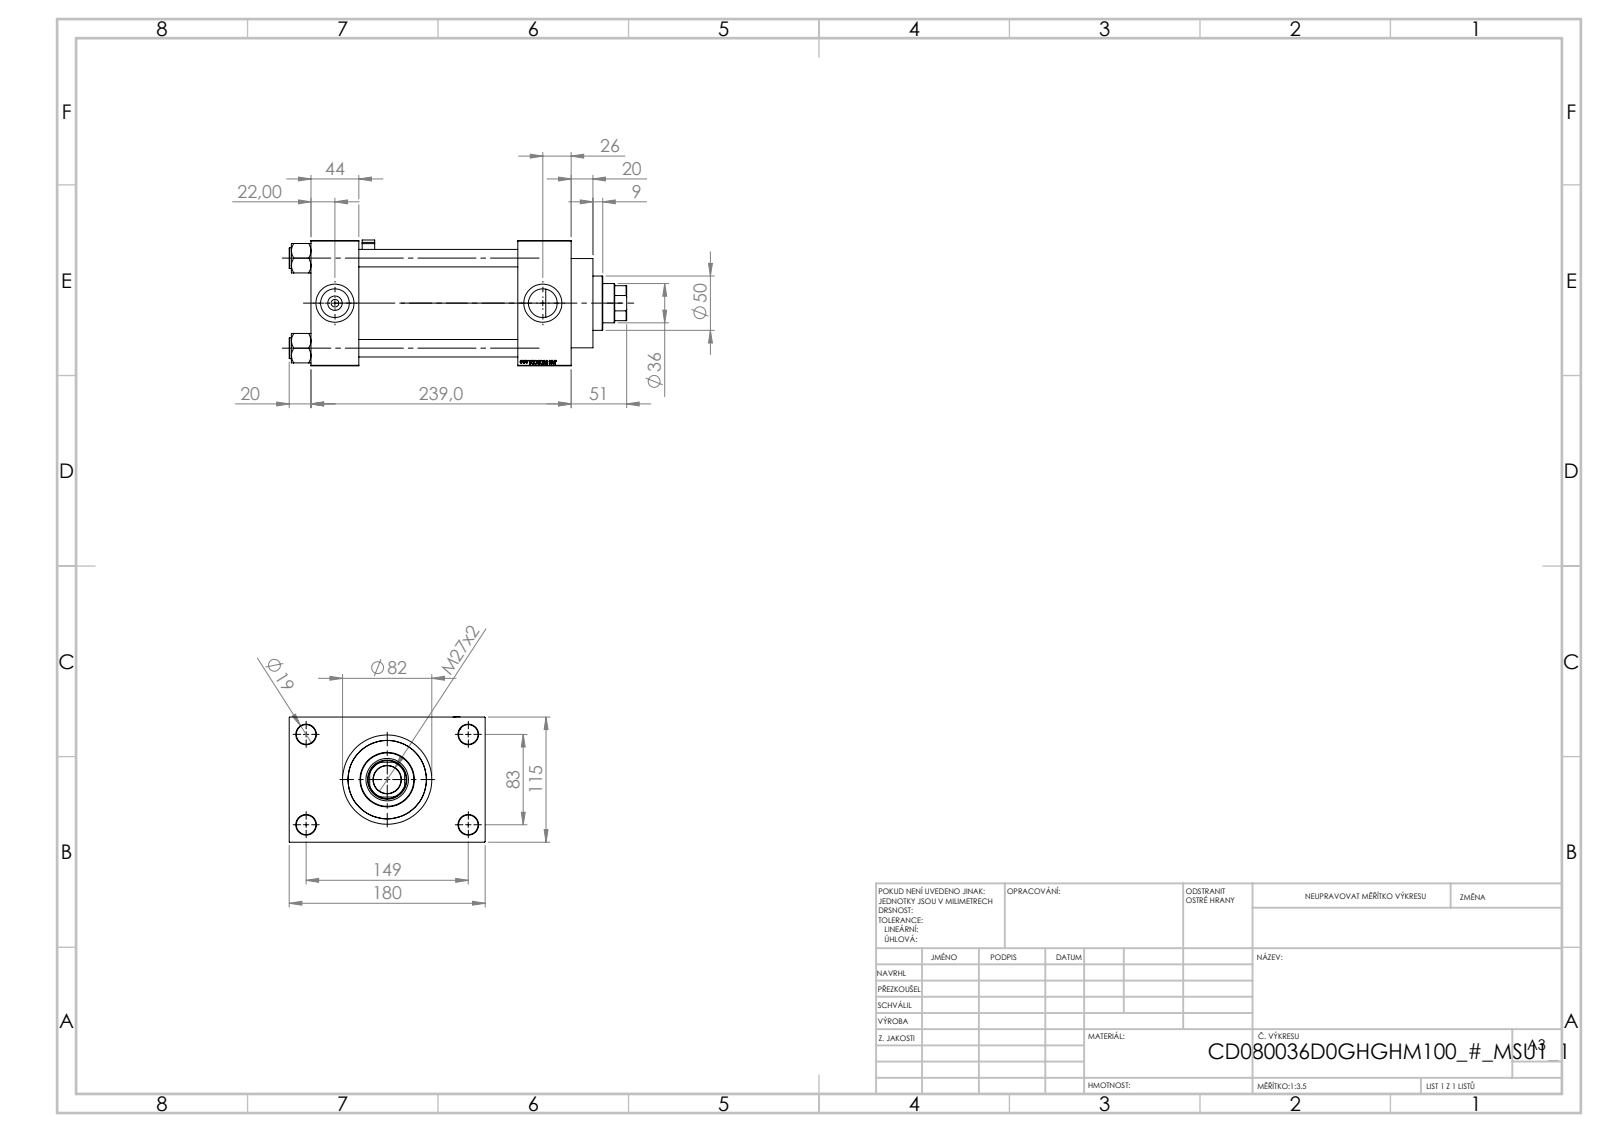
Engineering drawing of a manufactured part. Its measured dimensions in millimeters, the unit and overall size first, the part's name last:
Units: millimetres
Overall size (bounding box): 310 × 180 × 115.49
Round holes (diameter × count): ⌀16 ×4, ⌀18 ×4, ⌀7 ×2, ⌀26.44 ×2, ⌀35 ×2, ⌀25.5 ×1, ⌀36 ×1, ⌀39 ×1, ⌀61 ×1, ⌀72 ×1, ⌀80 ×1
Round bosses / shafts (diameter × count): ⌀19 ×4, ⌀86 ×1, ⌀82 ×1, ⌀50 ×1, ⌀6 ×1
Partial cylindrical surfaces — rounded edges, fillets, slot ends (radius × count): R0.5 ×24, R1 ×1, R2.5 ×1, R4 ×1, R17.5 ×1
Main face-to-face distances: 115, 146, 195, 49, 44, 190, 239, 32.5, 147.5, 180
Hole centre spacings: 33.15, 58.48, 82.7, 85.28, 89.24, 115.85, 142.43, 83
Volume: 2 208 000 mm³ · Surface area: 369 673 mm²
Bodies: 12 solids, 1228 faces (574 planar, 118 cylindrical, 536 other)
Part name (STEP PRODUCT): V215CD_VCP_D; V215CD_D_Body; V215CD_VC_A; V215CD_D_TYCINKA (+2 more)
STEP written by: SolidWorks 2019 (CONFIG_CONTROL_DESIGN)
